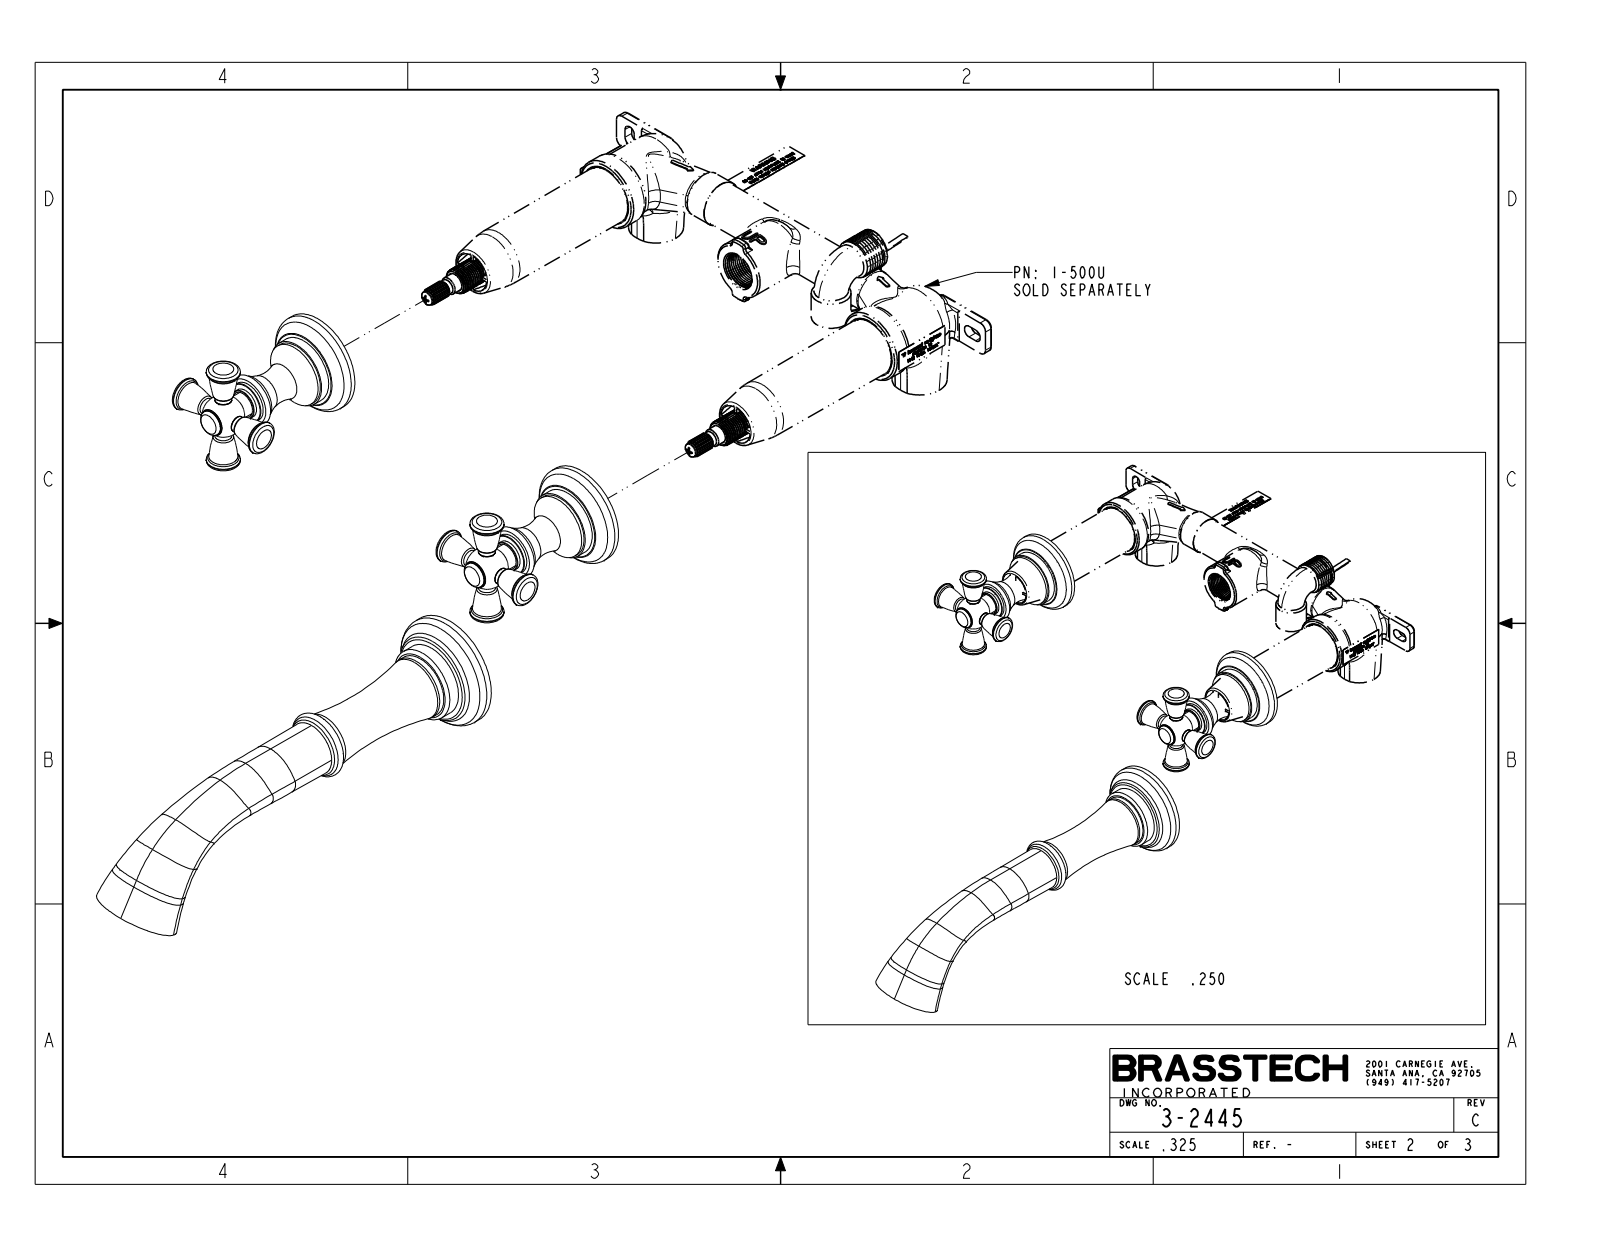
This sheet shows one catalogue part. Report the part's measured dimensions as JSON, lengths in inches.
{"part_name": "3-2445_SW0001", "step_written_by": "CREO PARAMETRIC BY PTC INC, 2018400 (AUTOMOTIVE_DESIGN)", "units": "inches", "bodies": {"solids": 3, "faces": 333, "planar": 25, "cylindrical": 66, "other": 242}, "overall_size": [10.403, 9.83, 9.052], "volume_in3": 21.53, "surface_area_in2": 98.34, "round_bosses_or_shafts": [[0.72, 3], [0.36, 3], [2.2, 2], [1.49, 2], [1.42, 2], [0.9, 2], [0.66, 2], [0.56, 2]], "face_to_face_distances": [0.43, 0.08, 0.55, 0.12, 2.17, 1.74, 1.62, 2.09, 1.66, 1.54]}
